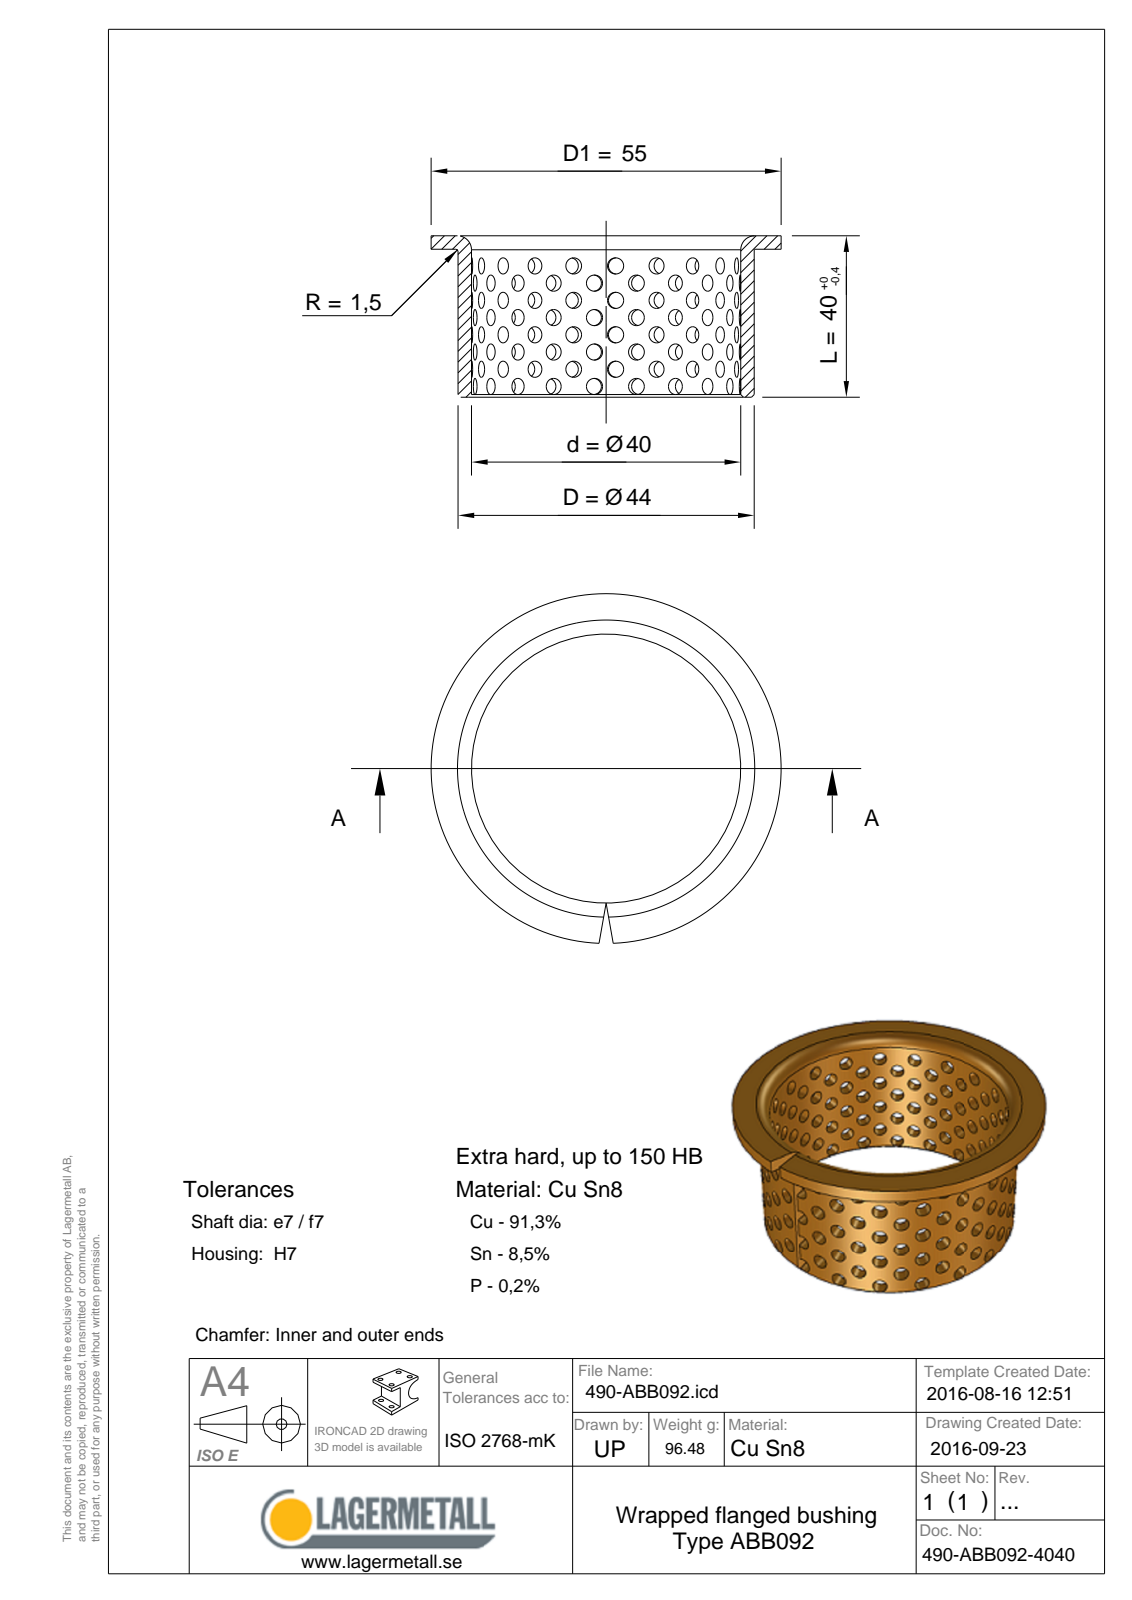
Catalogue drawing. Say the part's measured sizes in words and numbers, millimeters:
Its 3-D file was written by "Spatial InterOp 3D (CONFIG_CONTROL_DESIGN)". It is 1 solid with 25 faces: 5 planar, 8 cylindrical and 12 other. Overall it measures 55 by 55 by 40 millimeters. Its volume is 11 912 cubic millimeters and its surface area 12 643 square millimeters. Round holes: 1 of diameter 40. Round bosses or shafts: 1 of diameter 55, 1 of diameter 44. The main face-to-face distances are 2, 38, 40.
